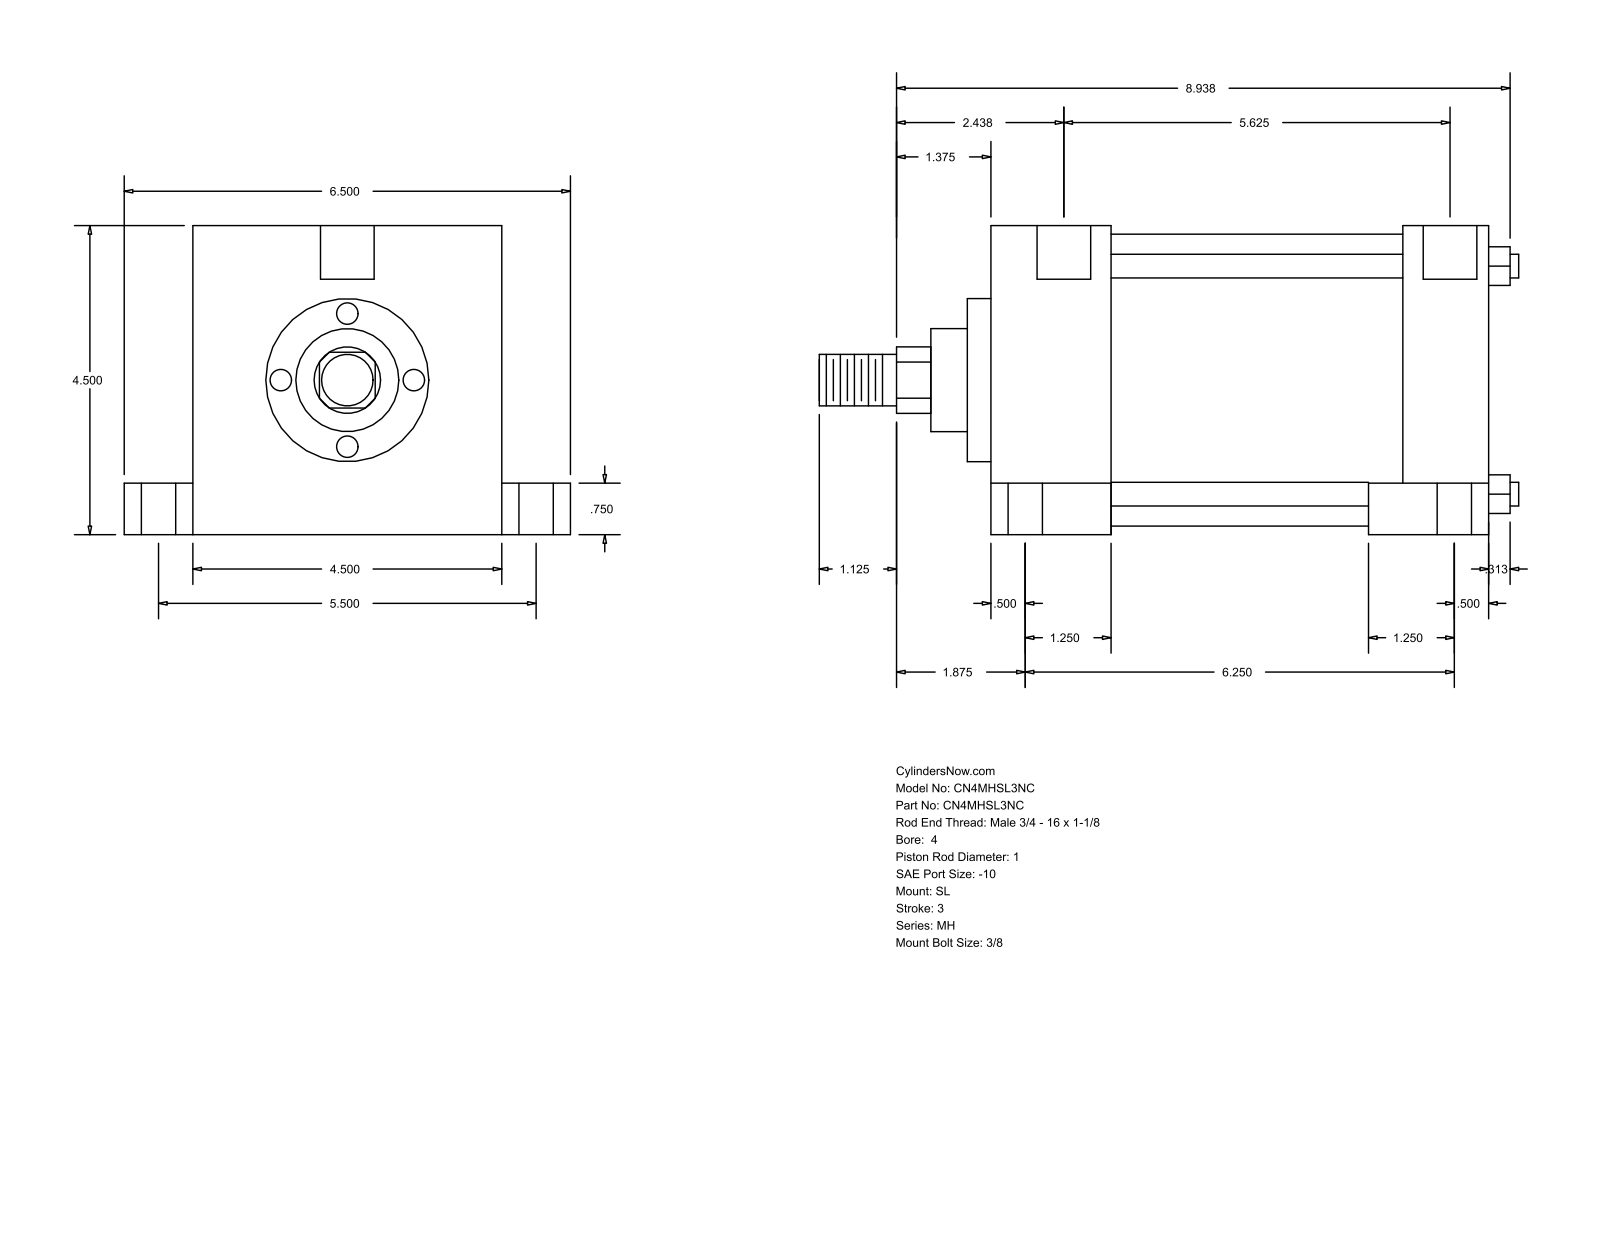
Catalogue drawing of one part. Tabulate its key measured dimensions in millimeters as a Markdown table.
| quantity | value |
| --- | --- |
| part name | MH_SL__0400_1 |
| STEP written by | GSSL Pune (CONFIG_CONTROL_DESIGN) |
| units | millimeters |
| bodies | 0 solids, 110 faces (77 planar, 33 cylindrical, 0 other) |
| overall size | 258.76 × 165.1 × 114.3 |
| round holes (diameter × count) | 8.73 × 4, 12.7 × 4, 19.05 × 4, 19.84 × 2 |
| round bosses / shafts (diameter × count) | 8.76 × 4, 107.95 × 1, 60.33 × 1, 38.1 × 1, 25.4 × 1, 19.05 × 1 |
| partial cylindrical surfaces (radius × count) | 12.29 × 1 |
| main face-to-face distances | 114.3, 184.15, 44.46, 139.69, 139.7, 152.4, 107.94, 31.75, 25.4, 19.05 |
| hole center spacings | 69.85, 69.87, 71, 71.3, 139.7, 146.05, 158.76, 160.47 |
